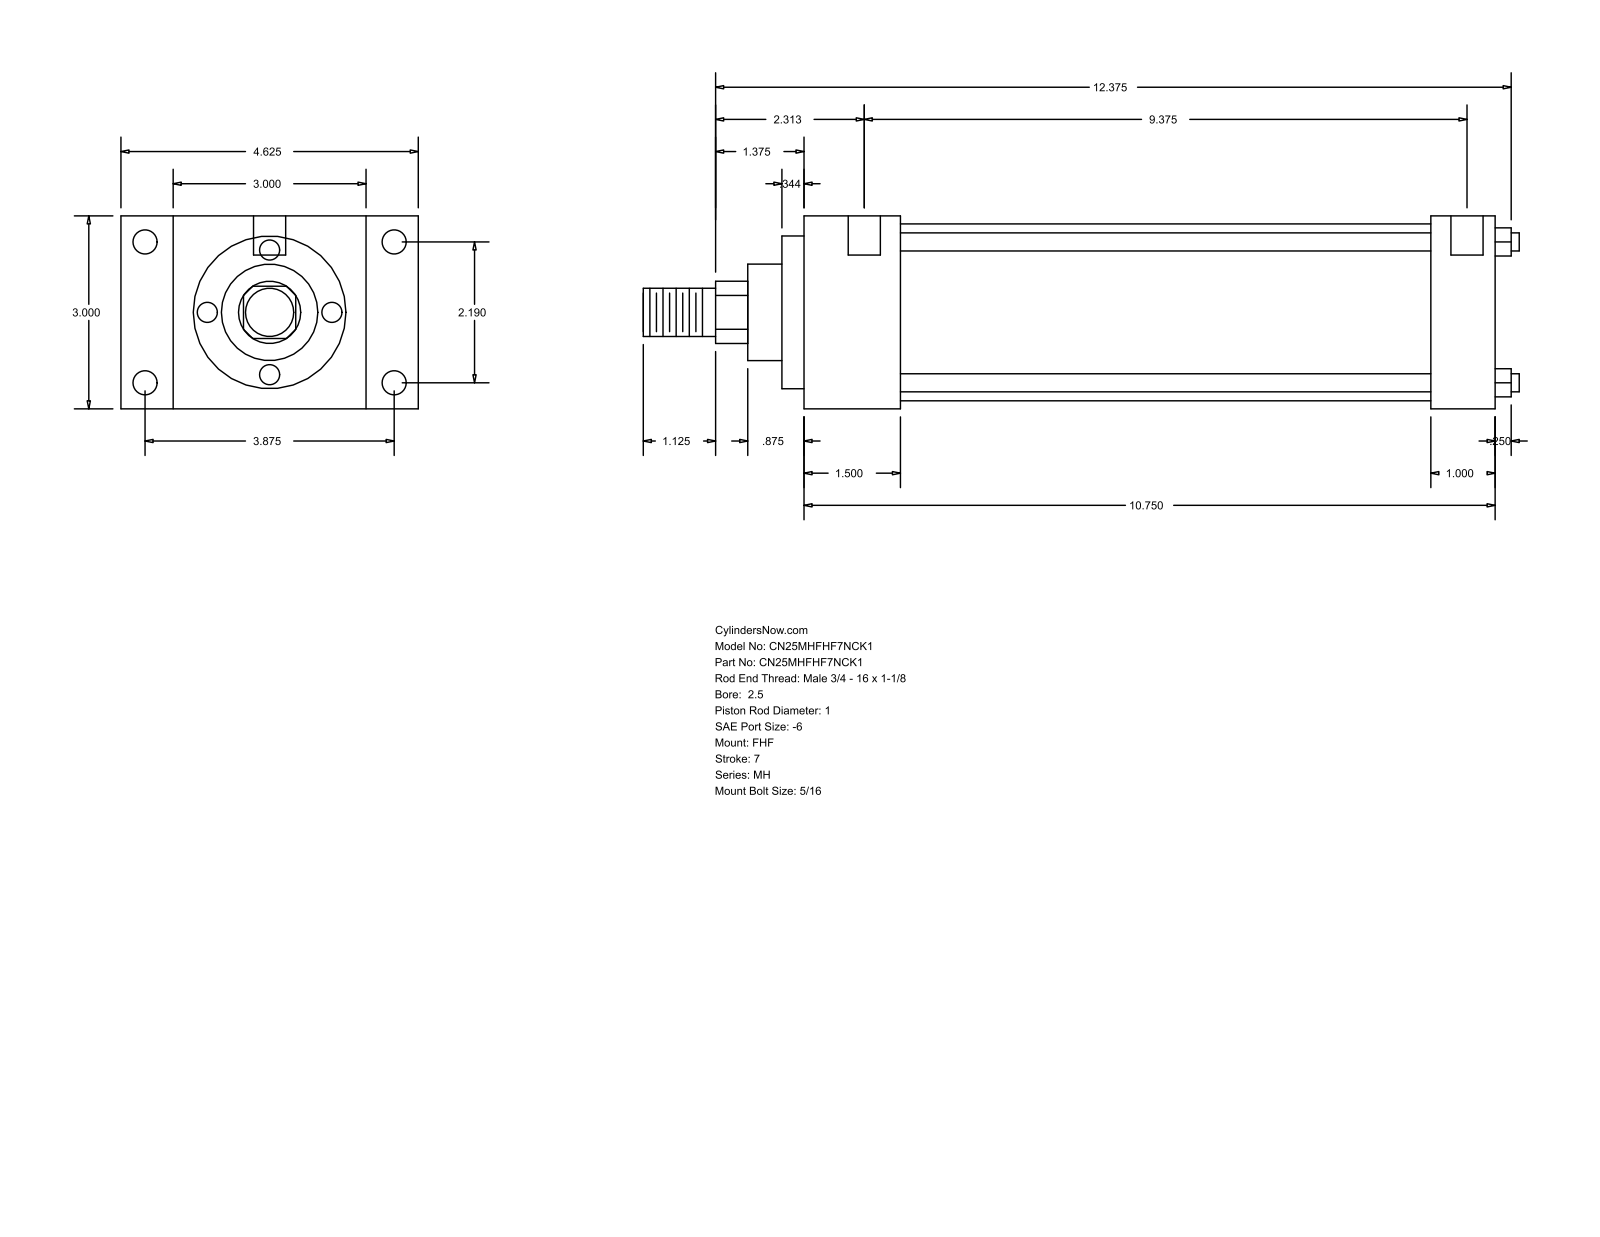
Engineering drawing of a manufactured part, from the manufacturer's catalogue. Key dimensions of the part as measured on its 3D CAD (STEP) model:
Part name (STEP PRODUCT): MH_FHF__0250_1
STEP written by: GSSL Pune (CONFIG_CONTROL_DESIGN)
Units: millimetres
Bodies: 0 solids, 90 faces (61 planar, 29 cylindrical, 0 other)
Overall size (bounding box): 346.07 × 117.47 × 76.2
Round holes (diameter × count): ⌀5.56 ×4, ⌀9.53 ×4, ⌀12.7 ×2
Round bosses / shafts (diameter × count): ⌀7.14 ×4, ⌀69.85 ×1, ⌀60.33 ×1, ⌀38.1 ×1, ⌀25.4 ×1, ⌀19.05 ×1
Partial cylindrical surfaces — rounded edges, fillets, slot ends (radius × count): R12.29 ×1
Main face-to-face distances: 76.2, 273.06, 38.11, 234.95, 20.64, 96.84, 117.48, 247.65, 209.54, 25.41
Hole centre spacings: 55.62, 98.42, 113.05, 246.06, 3.18, 4.76, 238.12, 241.3
